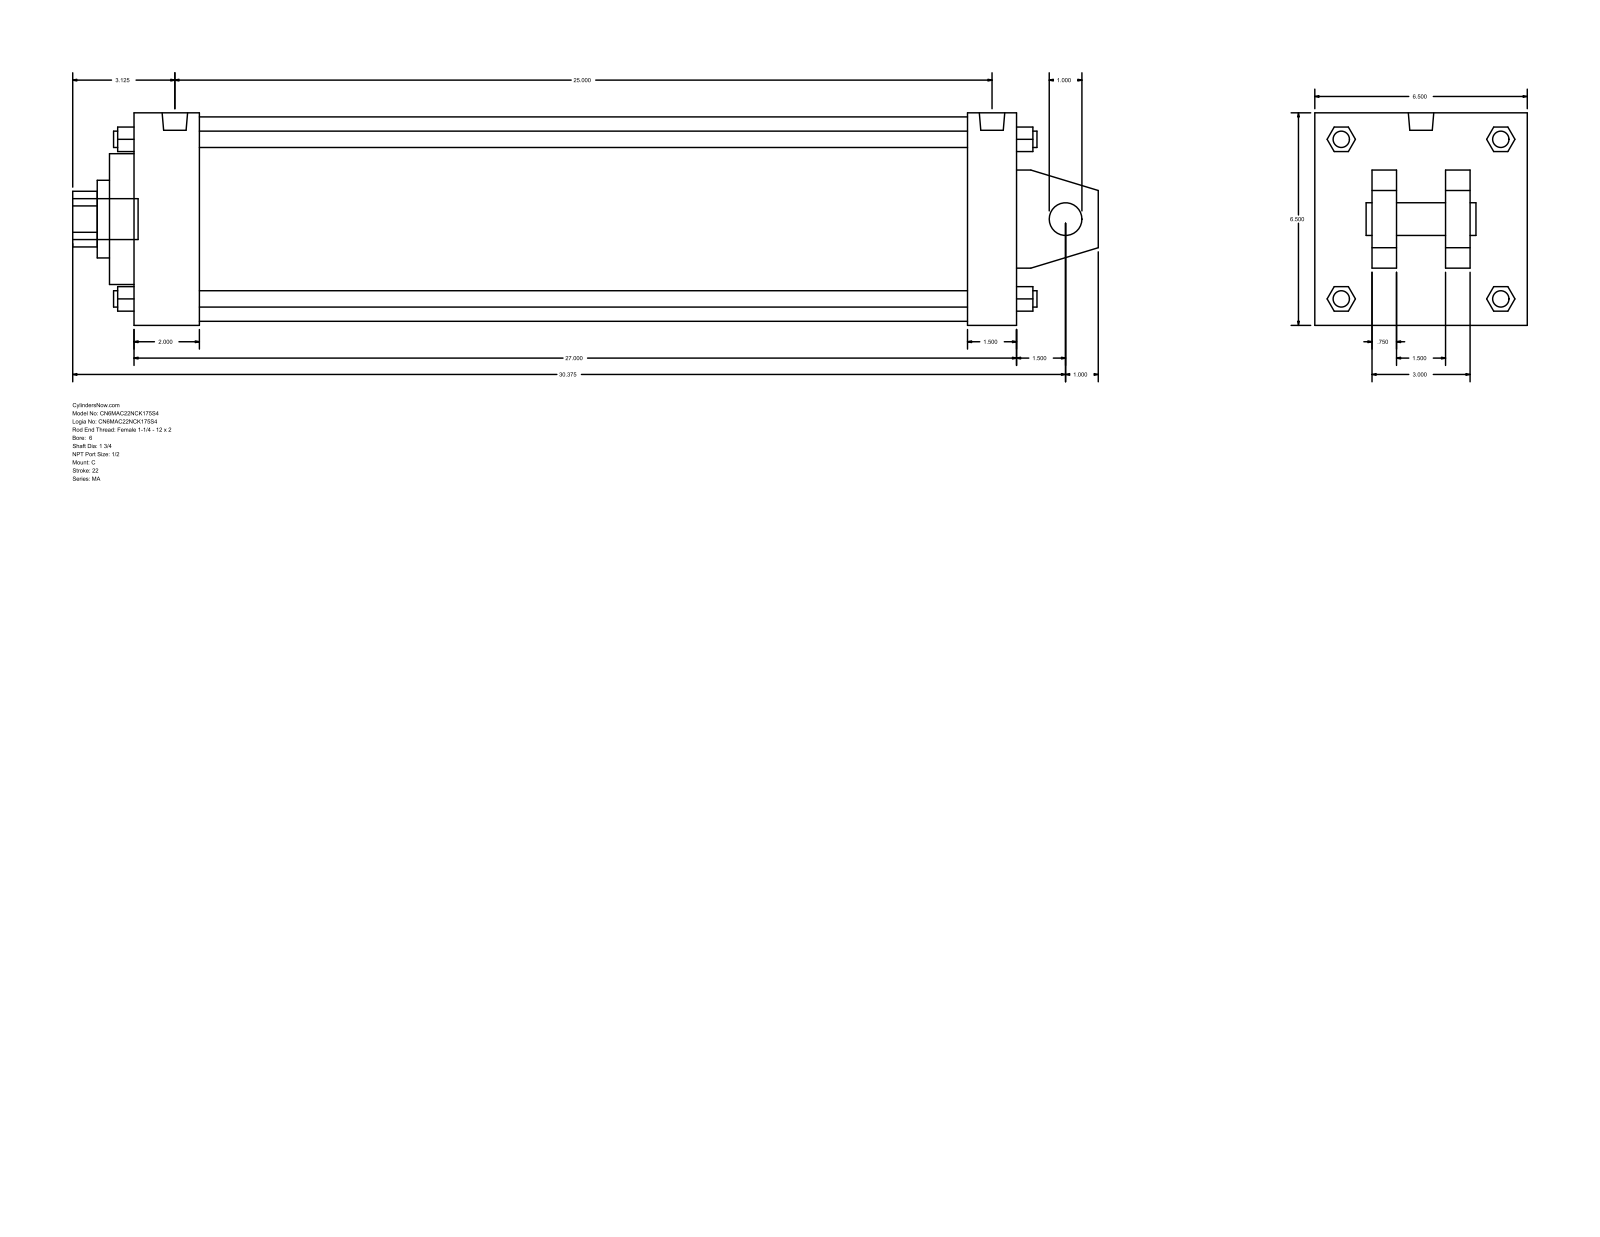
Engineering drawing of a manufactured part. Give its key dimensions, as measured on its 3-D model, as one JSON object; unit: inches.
{"part_name": "MA_C__0600_1.75", "step_written_by": "GSSL Pune (CONFIG_CONTROL_DESIGN)", "units": "inches", "bodies": {"solids": 0, "faces": 141, "planar": 109, "cylindrical": 32, "other": 0}, "overall_size": [31.375, 6.5, 6.5], "round_holes": [[1, 1], [1.75, 1], [2.375, 1], [4, 1], [6.25, 1]], "round_bosses_or_shafts": [[0.687, 4], [0.5, 4], [0.778, 2], [1.25, 1]], "partial_cylinders_radius": [[0.852, 1]], "face_to_face_distances": [6.5, 27, 0.75, 2.5, 4, 2, 1.75, 4.75, 2.25, 25]}
